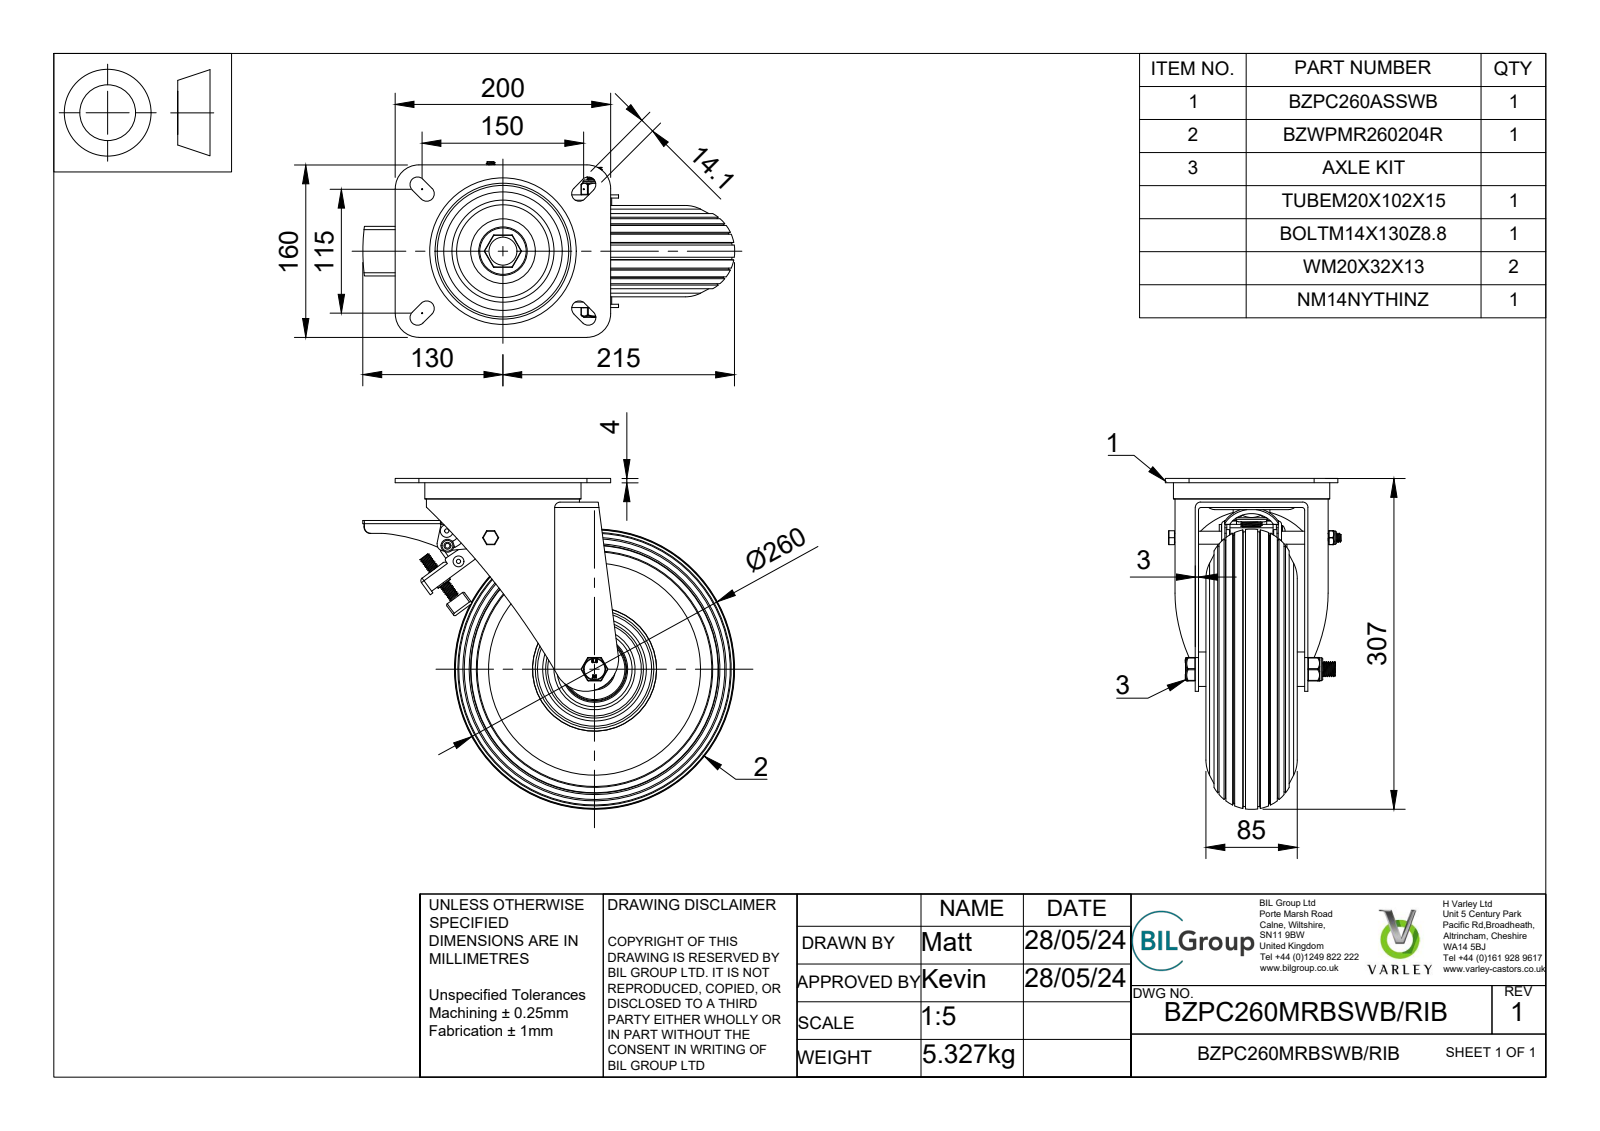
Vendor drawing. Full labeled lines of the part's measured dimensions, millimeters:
Part name (STEP PRODUCT): BZPC260MRBSWB/RIB v4; BZPC260ASSWB v1; PRESSED STEEL TOP PLATE; PRESSED STEEL TOP PLATE Geometry (+6 more)
STEP written by: Autodesk Translation Framework v13.14.0.145 (AUTOMOTIVE_DESIGN)
Units: millimetres
Bodies: 99 solids, 1006 faces (305 planar, 370 cylindrical, 331 other)
Overall size (bounding box): 345 × 307 × 163.09
Volume: 1 959 000 mm³ · Surface area: 919 925 mm²
Round holes (diameter × count): ⌀6 ×3, ⌀4 ×2, ⌀20 ×2, ⌀4.5 ×1, ⌀6.01 ×1, ⌀8.15 ×1, ⌀8.2 ×1, ⌀9 ×1, ⌀10 ×1, ⌀14 ×1, ⌀14.2 ×1, ⌀15.2 ×1
Round bosses / shafts (diameter × count): ⌀7.5 ×8, ⌀12 ×3, ⌀10 ×3, ⌀17 ×2, ⌀7 ×2, ⌀145 ×1, ⌀142 ×1, ⌀105.5 ×1
Partial cylindrical surfaces — rounded edges, fillets, slot ends (radius × count): R0.25 ×30, R0.5 ×18, R3 ×13, R1 ×8, R7.05 ×8, R1.25 ×6, R0.47 ×4, R0.9 ×4
Main face-to-face distances: 4, 3, 101.5, 11, 7, 5, 12, 16, 15.5, 6.5
Hole centre spacings: 13.77, 17.76, 30.28, 37.12, 40.84, 41.28, 41.78, 117.84
